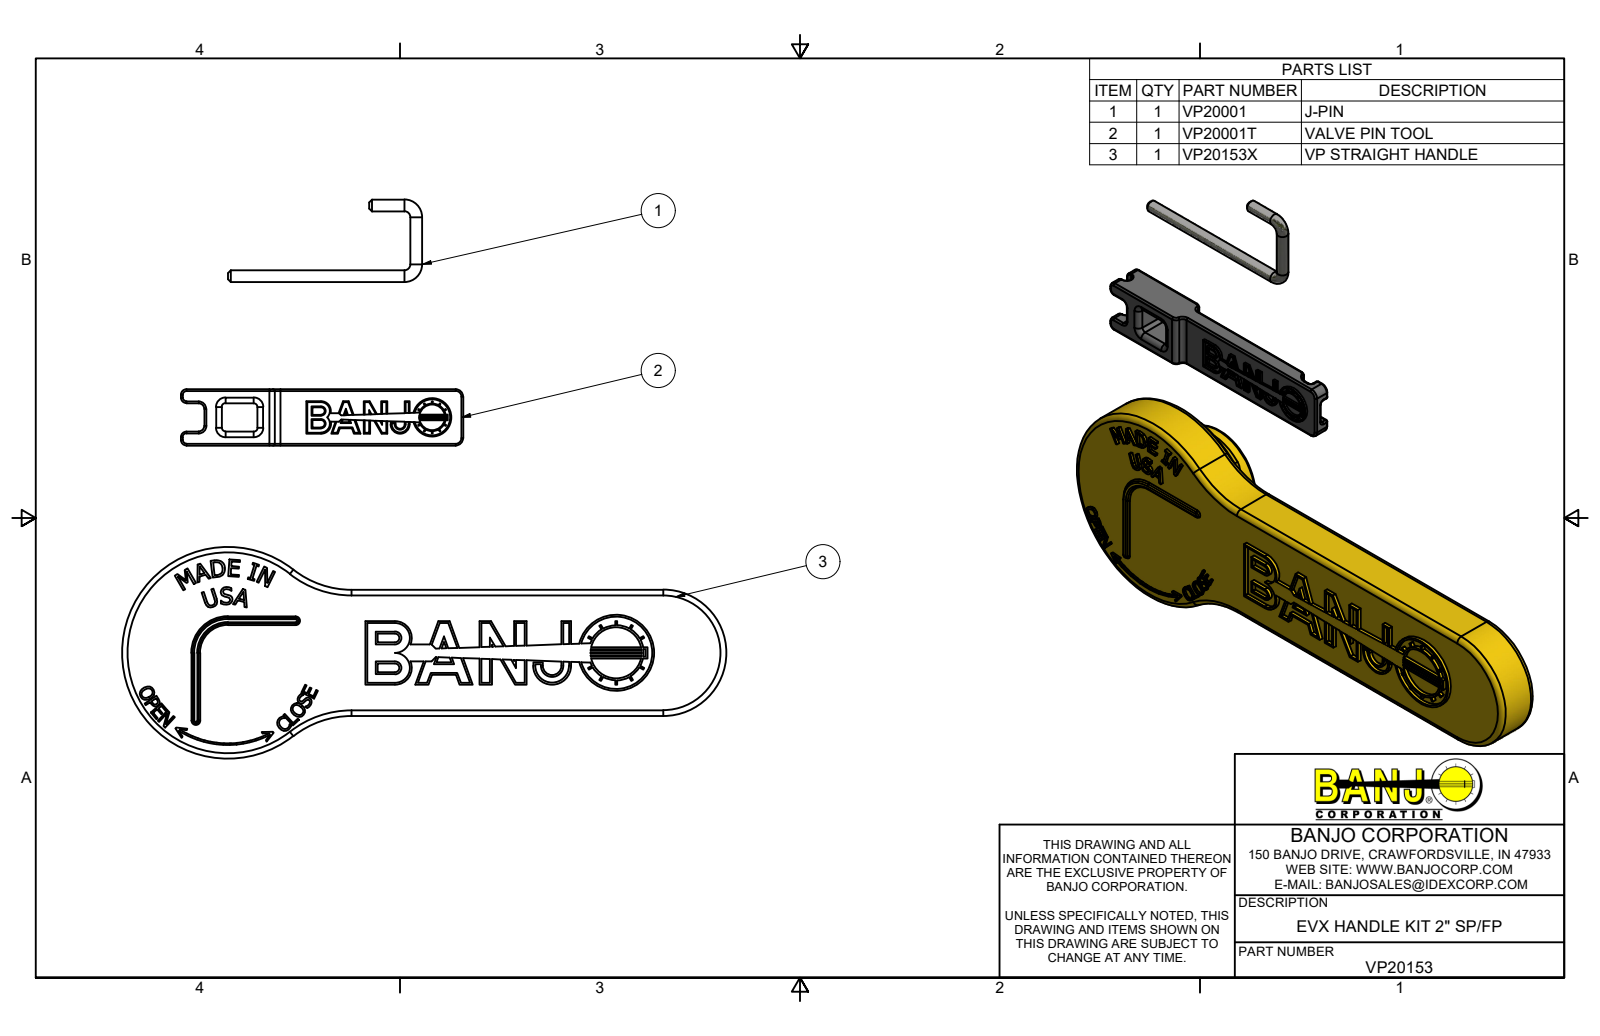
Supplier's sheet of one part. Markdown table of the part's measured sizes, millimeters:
| quantity | value |
| --- | --- |
| part name | VP20153; VP20153X; VP20001T; VP20001 |
| STEP written by | Autodesk Inventor 2021 (AUTOMOTIVE_DESIGN) |
| units | millimeters |
| bodies | 3 solids, 1330 faces (754 planar, 233 cylindrical, 343 other) |
| overall size | 163.1 × 150.8 × 29.5 |
| volume | 82 330 mm³ |
| surface area | 25 660 mm² |
| round holes (diameter × count) | 6.9 × 1, 9.8 × 1, 13.8 × 1, 19.6 × 1 |
| round bosses / shafts (diameter × count) | 3.2 × 3, 52.3 × 1, 20.6 × 1, 10.3 × 1 |
| partial cylindrical surfaces (radius × count) | 1.5 × 33, 0.5 × 28, 0.8 × 13, 0.3 × 10, 0.4 × 8, 1 × 4, 2.3 × 4, 3.2 × 4 |
| main face-to-face distances | 8.1, 14.3, 6.2, 34, 12.7, 3.4, 4.7, 9.6, 15.2, 8 |
| hole center spacings | 80.6 |
